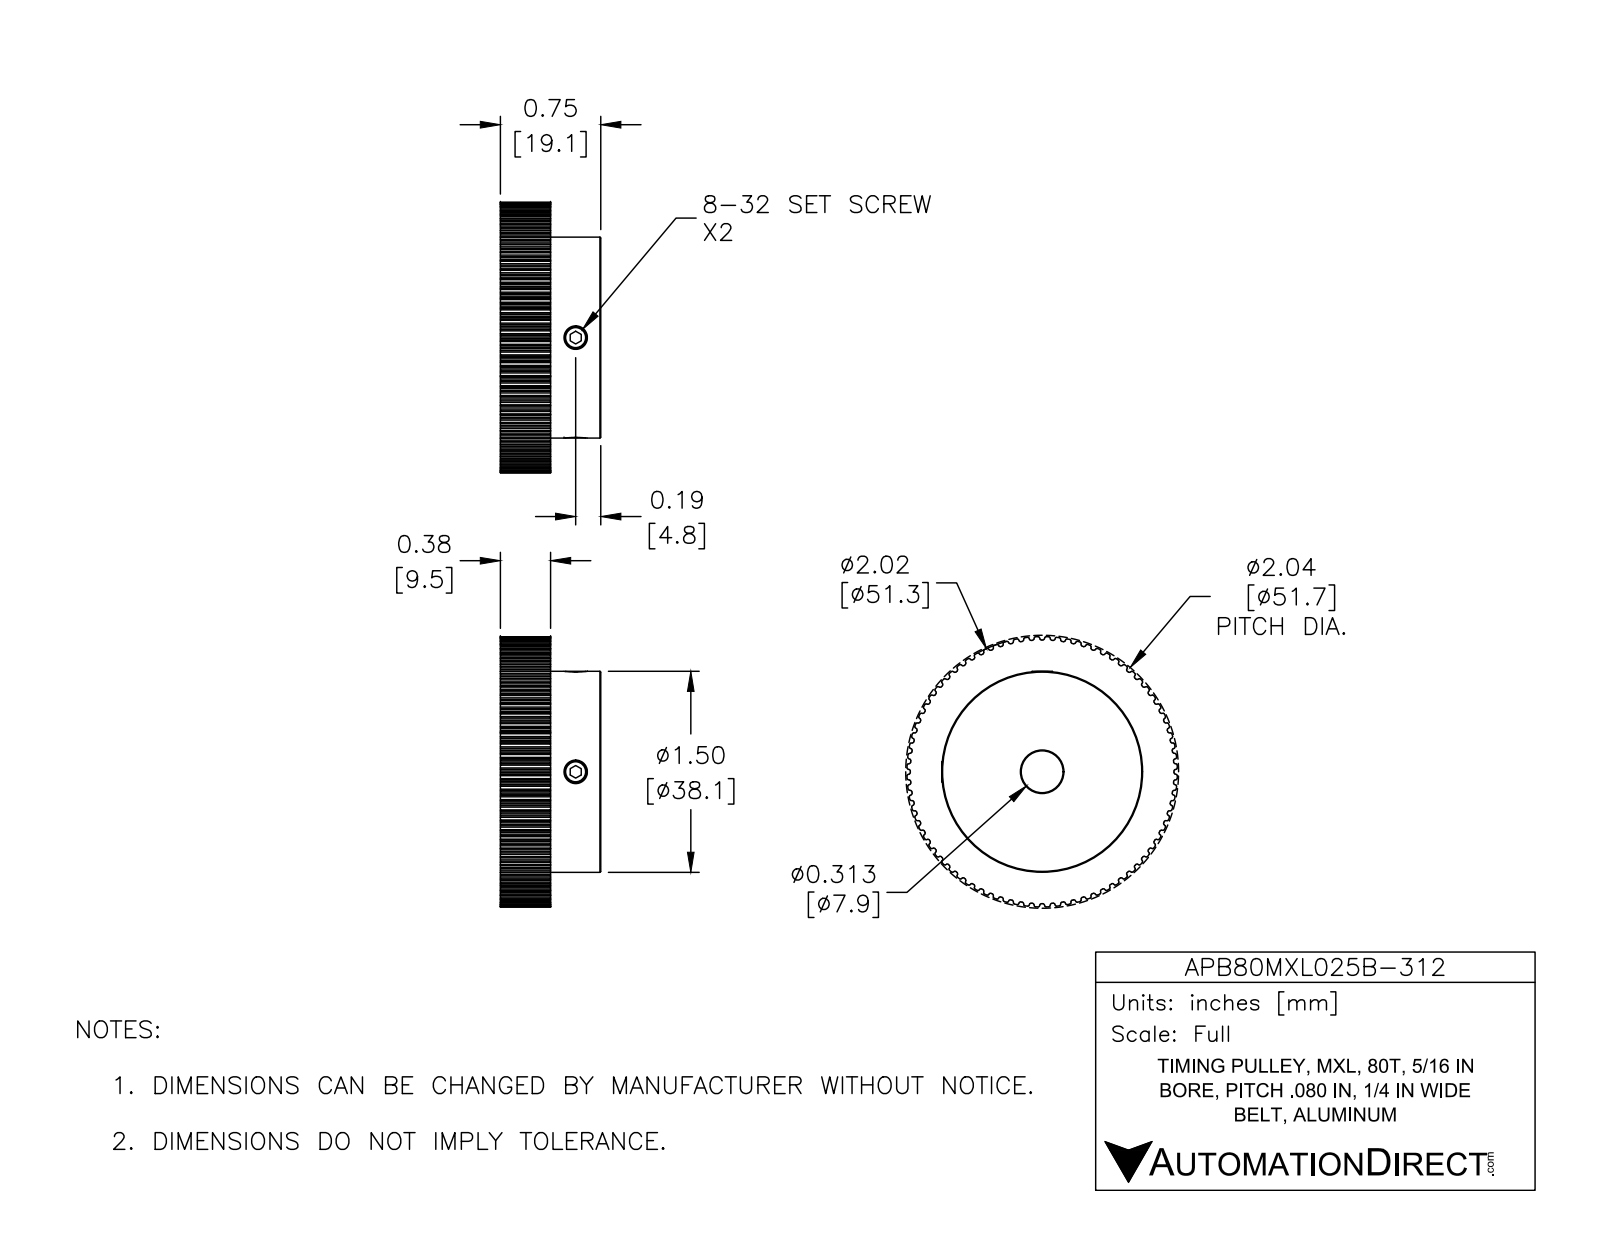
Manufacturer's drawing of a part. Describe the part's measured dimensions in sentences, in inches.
The part is named "APB80MXL025B-312". Its 3-D file was written by "SolidWorks 2016 (AUTOMOTIVE_DESIGN)". It is 3 solids with 749 faces: 261 planar, 474 cylindrical and 14 other. Overall it measures 2.017 by 2.017 by 0.75 inches. Its volume is 1.756 cubic inches and its surface area 12.49 square inches. Round holes: 2 of diameter 0.164, 1 of diameter 0.313. Round bosses or shafts: 2 of diameter 0.16, 1 of diameter 1.5. Partial cylindrical surfaces (rounded edges, fillets, slot ends): 160 of radius 0.009, 160 of radius 0.012, 1 of radius 1.009. The main face-to-face distances are 0.75, 0.375, 0.375, 0.648, 1.968, 0.647, 1.969, 0.649, 0.646, 1.967.
